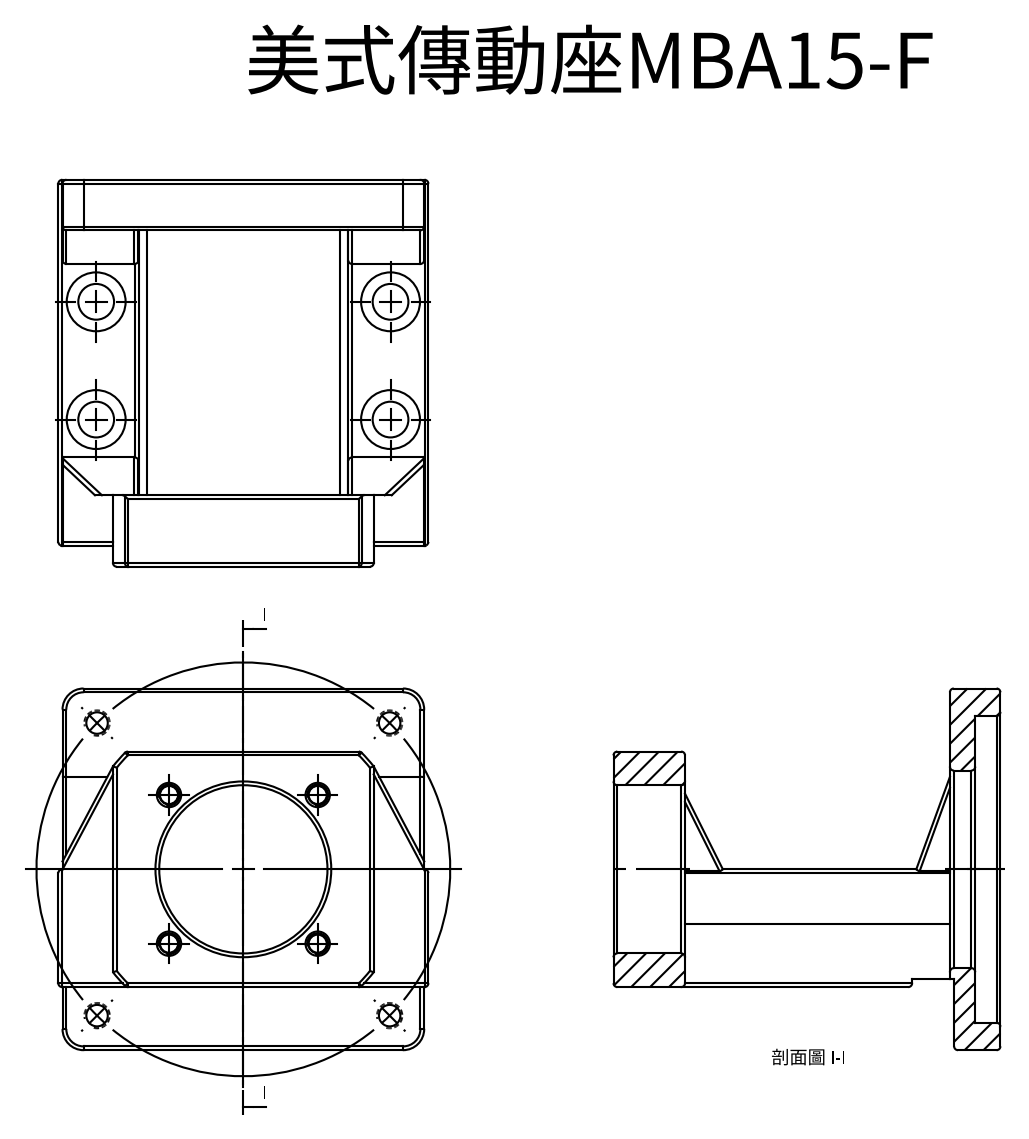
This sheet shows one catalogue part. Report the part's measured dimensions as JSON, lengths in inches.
{"part_name": "美式傳動座MBA15-F", "step_written_by": "SolidWorks 2011 (AUTOMOTIVE_DESIGN)", "units": "inches", "bodies": {"solids": 1, "faces": 253, "planar": 49, "cylindrical": 114, "other": 90}, "overall_size": [3.622, 3.465, 3.386], "volume_in3": 10.37, "surface_area_in2": 68.27, "round_holes": [[0.169, 4], [0.201, 4], [0.335, 4], [0.551, 4], [0.228, 2], [0.236, 2], [1.575, 1], [1.85, 1], [2.874, 1]], "partial_cylinders_radius": [[0.035, 52], [0.197, 4], [1.555, 1]], "face_to_face_distances": [0.236, 0.472, 3.386, 0.039, 2.953, 0.197, 3.189, 3.465, 3.425, 2.717], "hole_center_spacings": [2.173, 0.551, 0.953, 0.984, 1.392, 1.937, 2.739, 2.811]}
